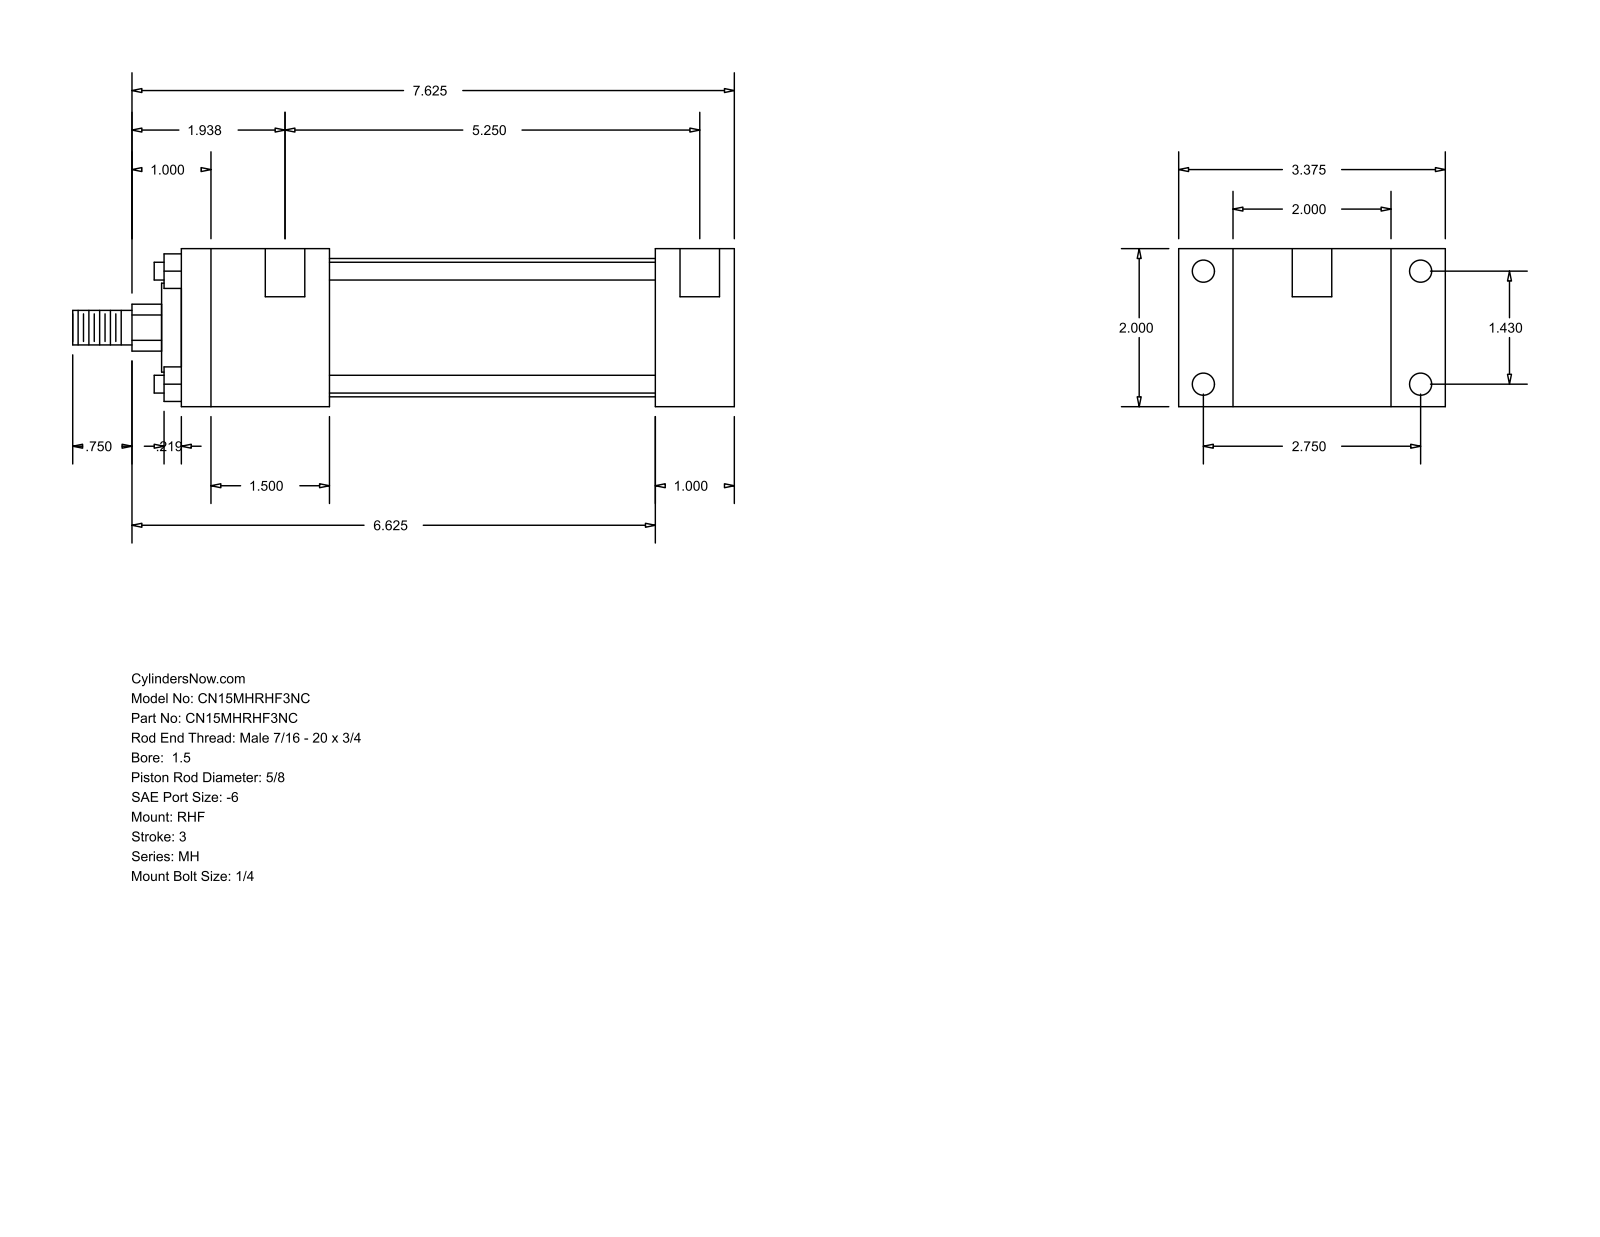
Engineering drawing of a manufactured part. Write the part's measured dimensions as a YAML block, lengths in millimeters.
part_name: "MH_RHF__0150_0.625"
step_written_by: "GSSL Pune (CONFIG_CONTROL_DESIGN)"
units: millimeters
bodies: {solids: 0, faces: 88, planar: 60, cylindrical: 28, other: 0}
overall_size: [212.72, 85.72, 50.8]
round_holes:
  - {diameter: 5.56, count: 4}
  - {diameter: 7.14, count: 4}
  - {diameter: 12.7, count: 2}
round_bosses_or_shafts:
  - {diameter: 5.71, count: 4}
  - {diameter: 44.45, count: 1}
  - {diameter: 28.57, count: 1}
  - {diameter: 15.88, count: 1}
  - {diameter: 11.11, count: 1}
partial_cylinders:
  - {radius: 7.54, count: 1}
face_to_face_distances: [50.8, 25.4, 17.46, 68.26, 152.4, 177.8, 85.72, 47.62, 104.78, 130.18]
hole_center_spacings: [36.32, 69.84, 78.72, 136.52, 3.17, 133.35]
